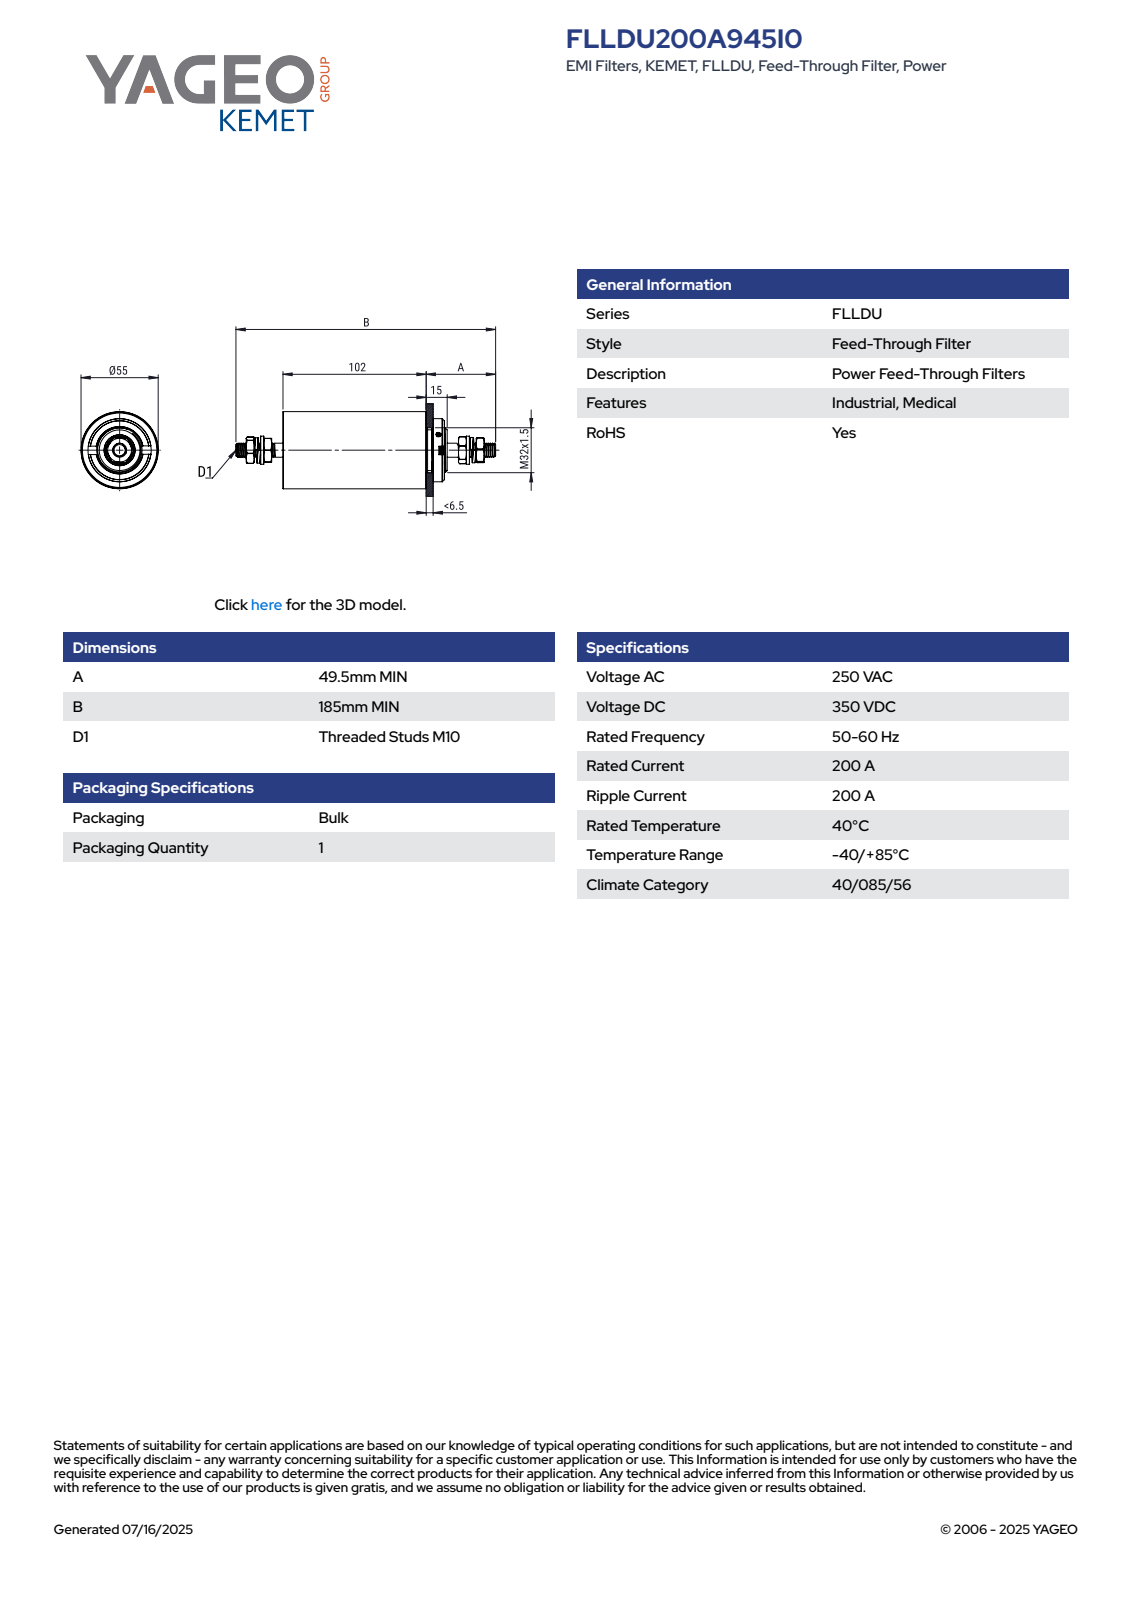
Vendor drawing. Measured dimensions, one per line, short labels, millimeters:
name: KLM0036_90592A024; DIC0027; FLLDU200A026I0; DIC0029 (+5 more)
written by: SolidWorks 2021 (AUTOMOTIVE_DESIGN)
unit: mm
bodies: 14 solids, 534 faces (63 planar, 241 cylindrical, 230 other)
size: 185 × 55 × 55
volume: 60 832 mm³; area: 64 969 mm²
holes: 2× ⌀3.2, 1× ⌀10.5, 1× ⌀22, 1× ⌀30.7, 1× ⌀53
bosses: 1× ⌀55, 1× ⌀54, 1× ⌀45, 1× ⌀32, 1× ⌀29, 1× ⌀22.1, 1× ⌀20, 1× ⌀10
rounds: 24× R0.25
face distances: 4, 101.5, 97.5, 8, 102.5, 110.5, 5, 106.5, 10, 13
